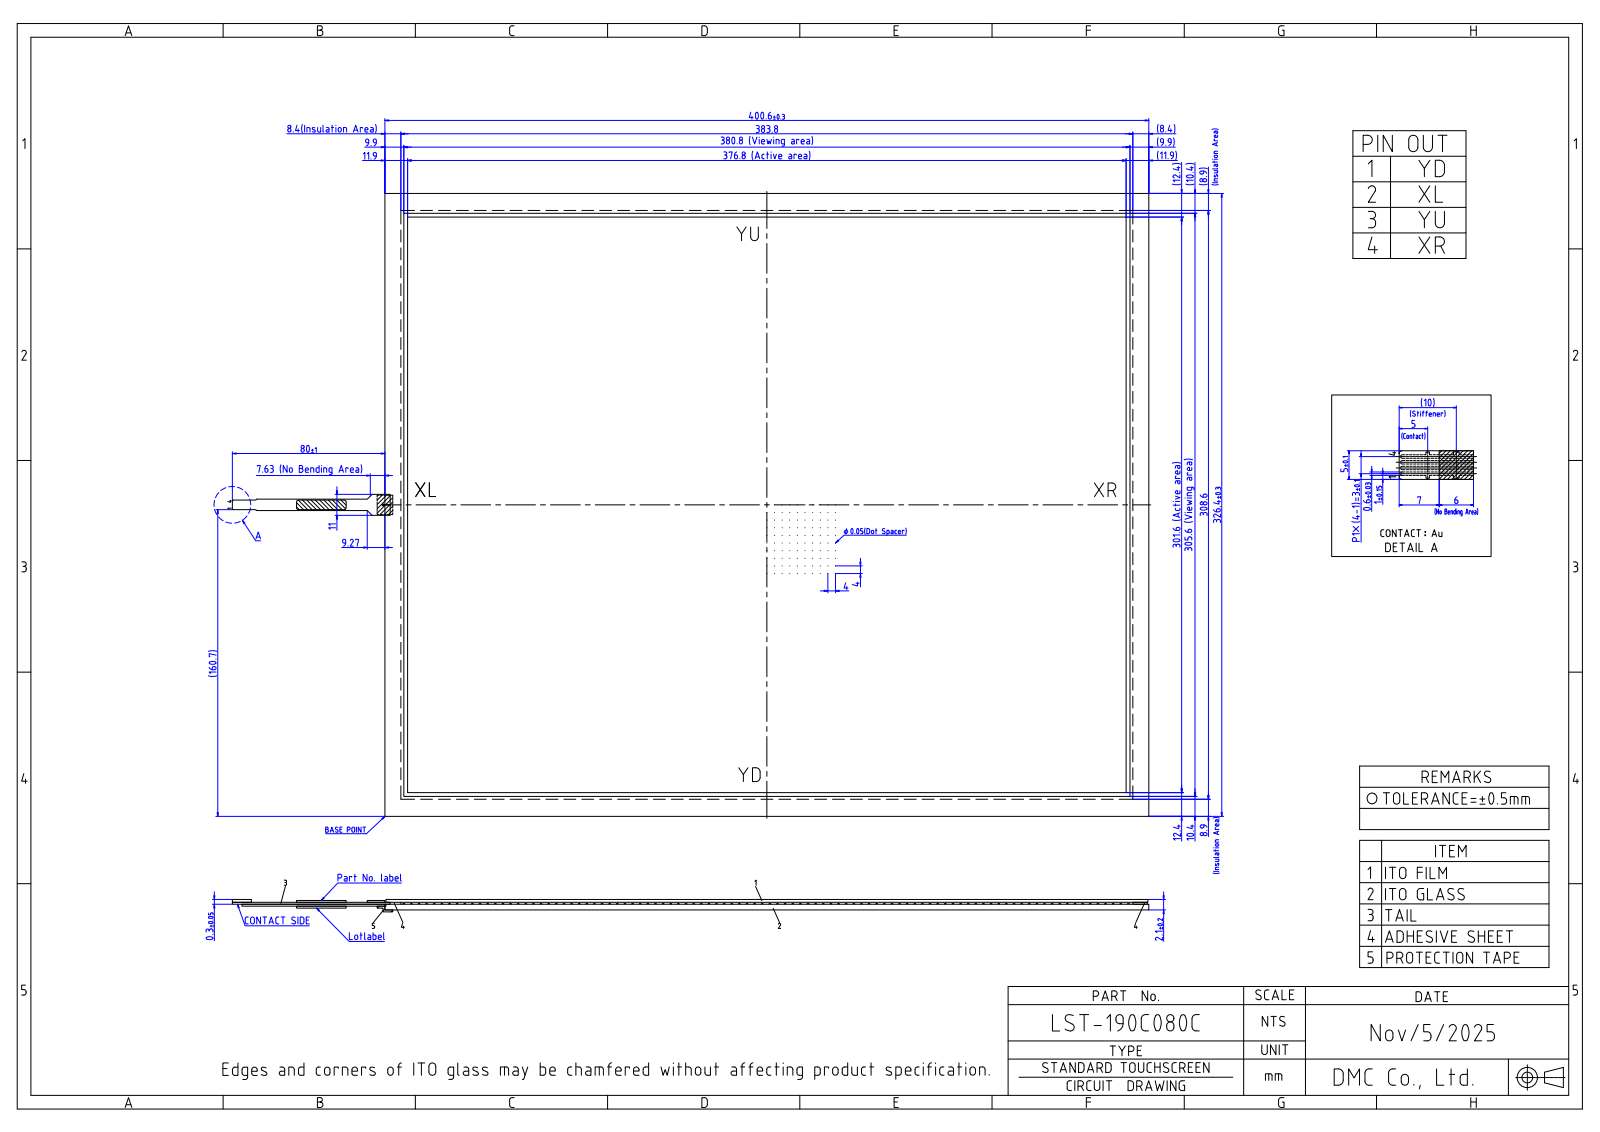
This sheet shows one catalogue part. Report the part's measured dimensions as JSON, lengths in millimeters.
{"part_name": "LST-190C080C-1", "step_written_by": "Autodesk Inventor 2020 (CONFIG_CONTROL_DESIGN)", "units": "millimeters", "bodies": {"solids": 2, "faces": 52, "planar": 46, "cylindrical": 6, "other": 0}, "overall_size": [560.84, 456.96, 2.6], "volume_mm3": 274377, "surface_area_mm2": 265879, "partial_cylinders_radius": [[0.3, 4], [0.5, 2]], "face_to_face_distances": [2.1, 2, 326.4, 400.6, 2.2, 2.3, 10.4, 316, 12.4, 314]}
